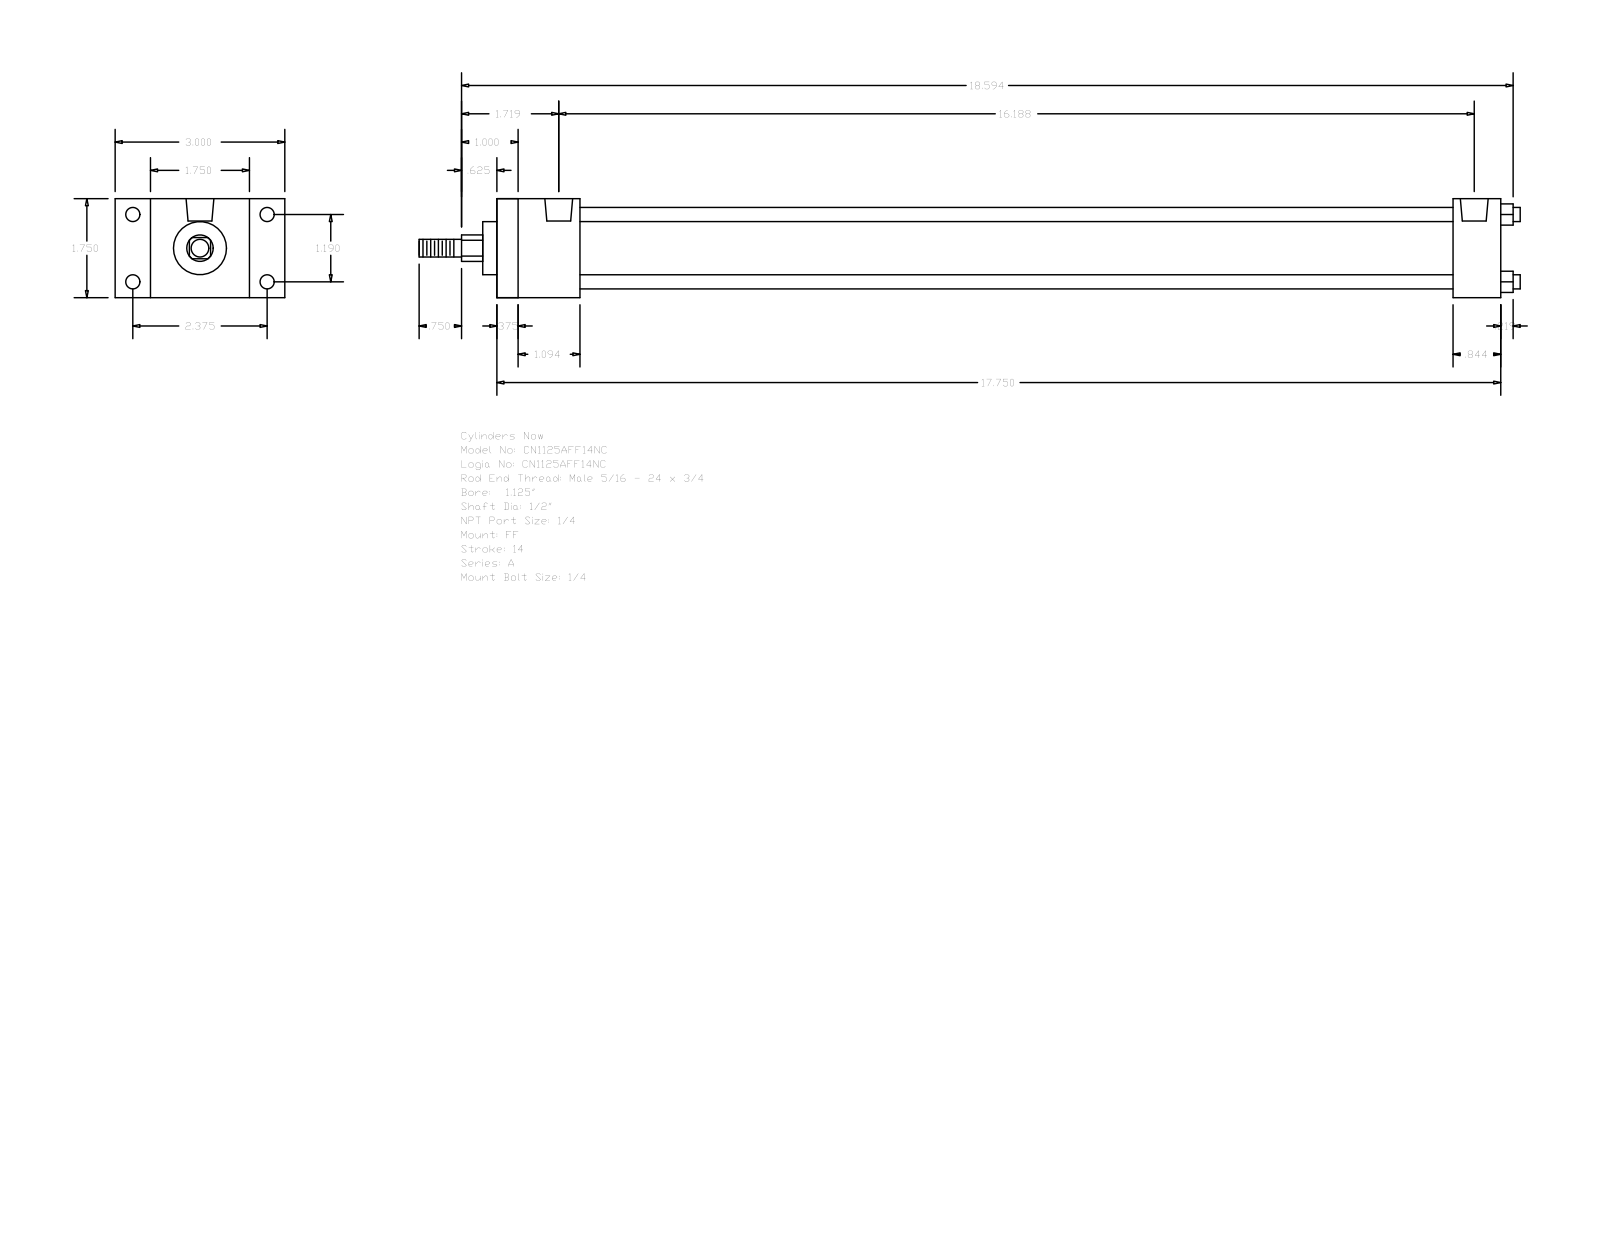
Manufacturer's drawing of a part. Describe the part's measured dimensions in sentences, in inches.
The part is named "A_FF__0112_0.5". Its 3-D file was written by "GSSL Pune (CONFIG_CONTROL_DESIGN)". It is 0 solids with 92 faces: 64 planar, 28 cylindrical and 0 other. Overall it measures 19.469 by 3 by 1.75 inches. Round holes: 4 of diameter 0.219, 4 of diameter 0.25, 2 of diameter 0.492. Round bosses or shafts: 4 of diameter 0.25, 1 of diameter 1.255, 1 of diameter 0.937, 1 of diameter 0.5, 1 of diameter 0.313. Partial cylindrical surfaces (rounded edges, fillets, slot ends): 1 of radius 0.234. The main face-to-face distances are 1.75, 17.75, 0.375, 17.375, 0.625, 16.906, 16.531, 0.844, 1.469, 1.094. The hole center spacings are 1.19, 2.375, 2.656, 16.063, 0.062, 0.063, 16.125, 16.125.
